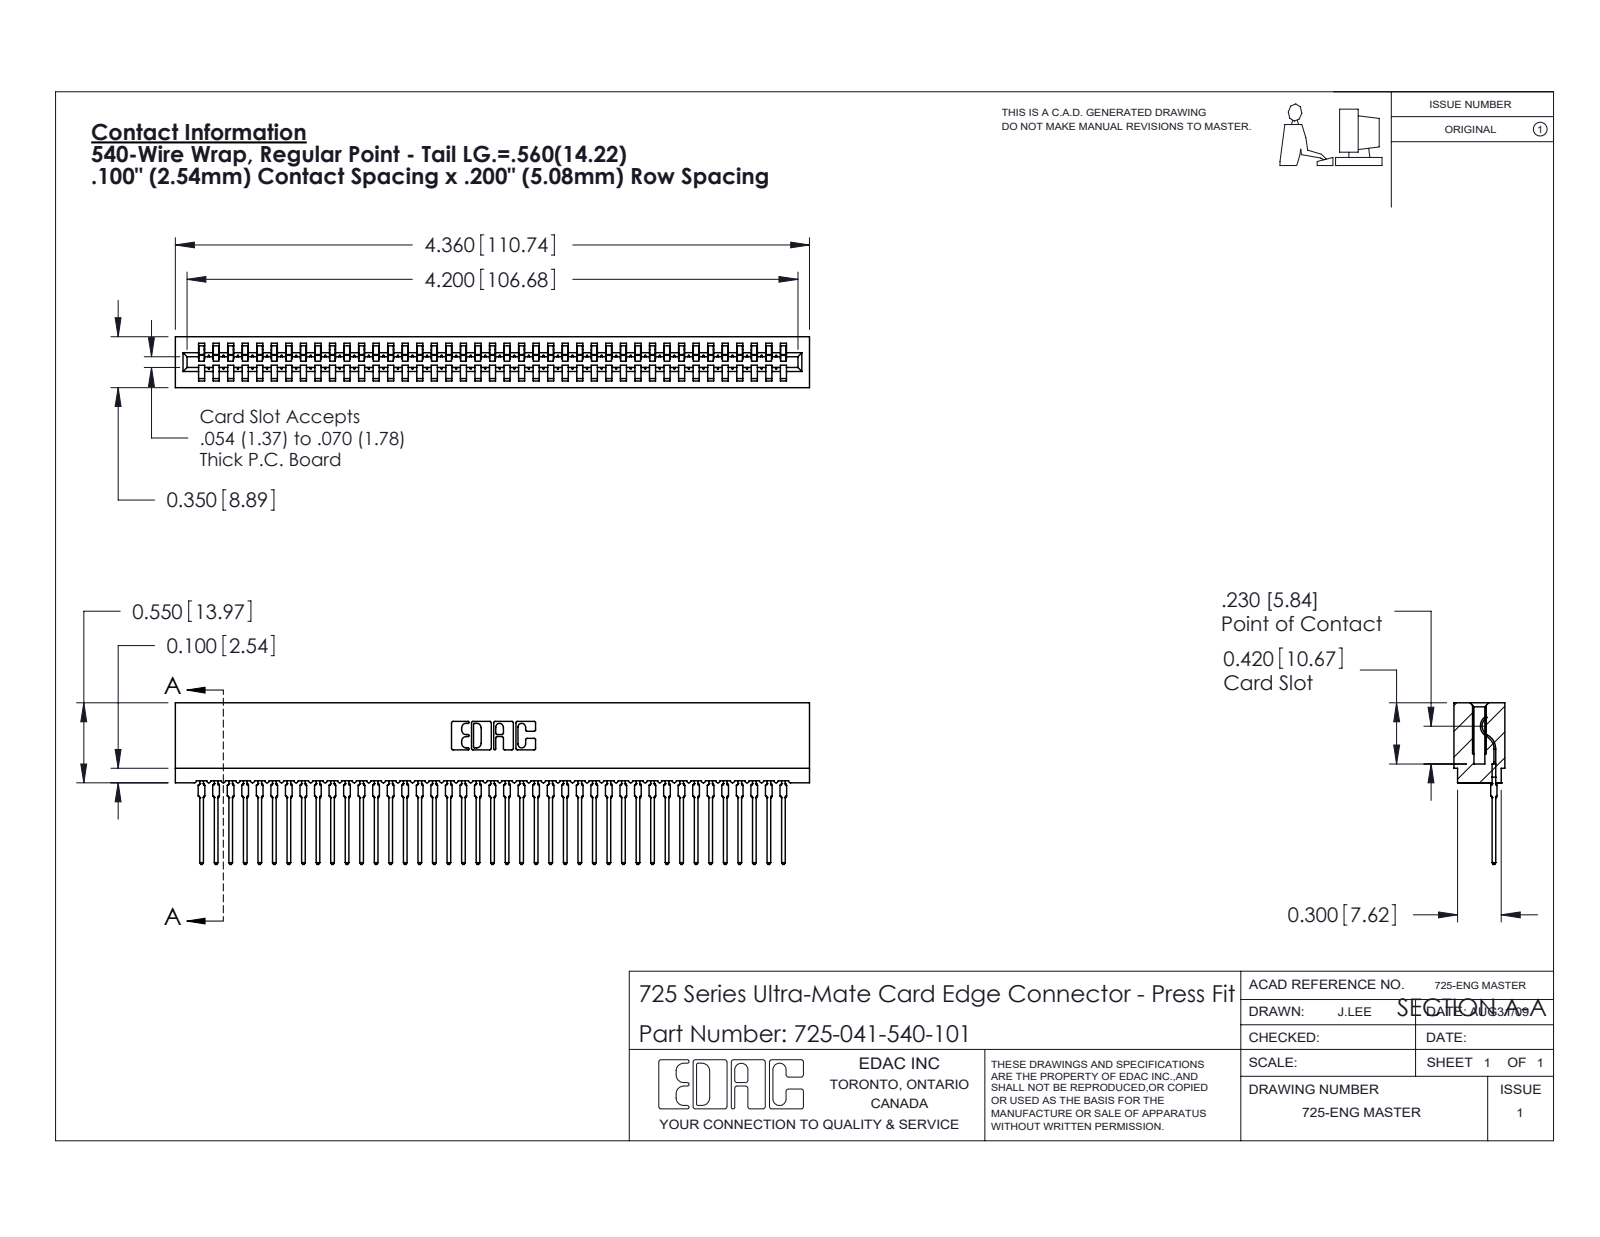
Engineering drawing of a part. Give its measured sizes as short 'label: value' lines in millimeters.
name: 745-292-001_540; 725 Part_Insulator Option - 01; 725-041-540-101
written by: SolidWorks 2020 (CONFIG_CONTROL_DESIGN)
unit: mm
bodies: 42 solids, 4687 faces (2802 planar, 819 cylindrical, 1066 other)
size: 110.7 × 28.2 × 8.9
volume: 8 500 mm³; area: 16 800 mm²
rounds: 82× R0.4, 82× R0.5, 22× R0.3, 6× R0.2, 6× R0.8, 4× R0.1, 4× R0.3, 3× R0.7
face distances: 8.9, 5.1, 2.5, 5.4, 3.5, 1.6, 7.3, 1.1, 7.7, 2.4
